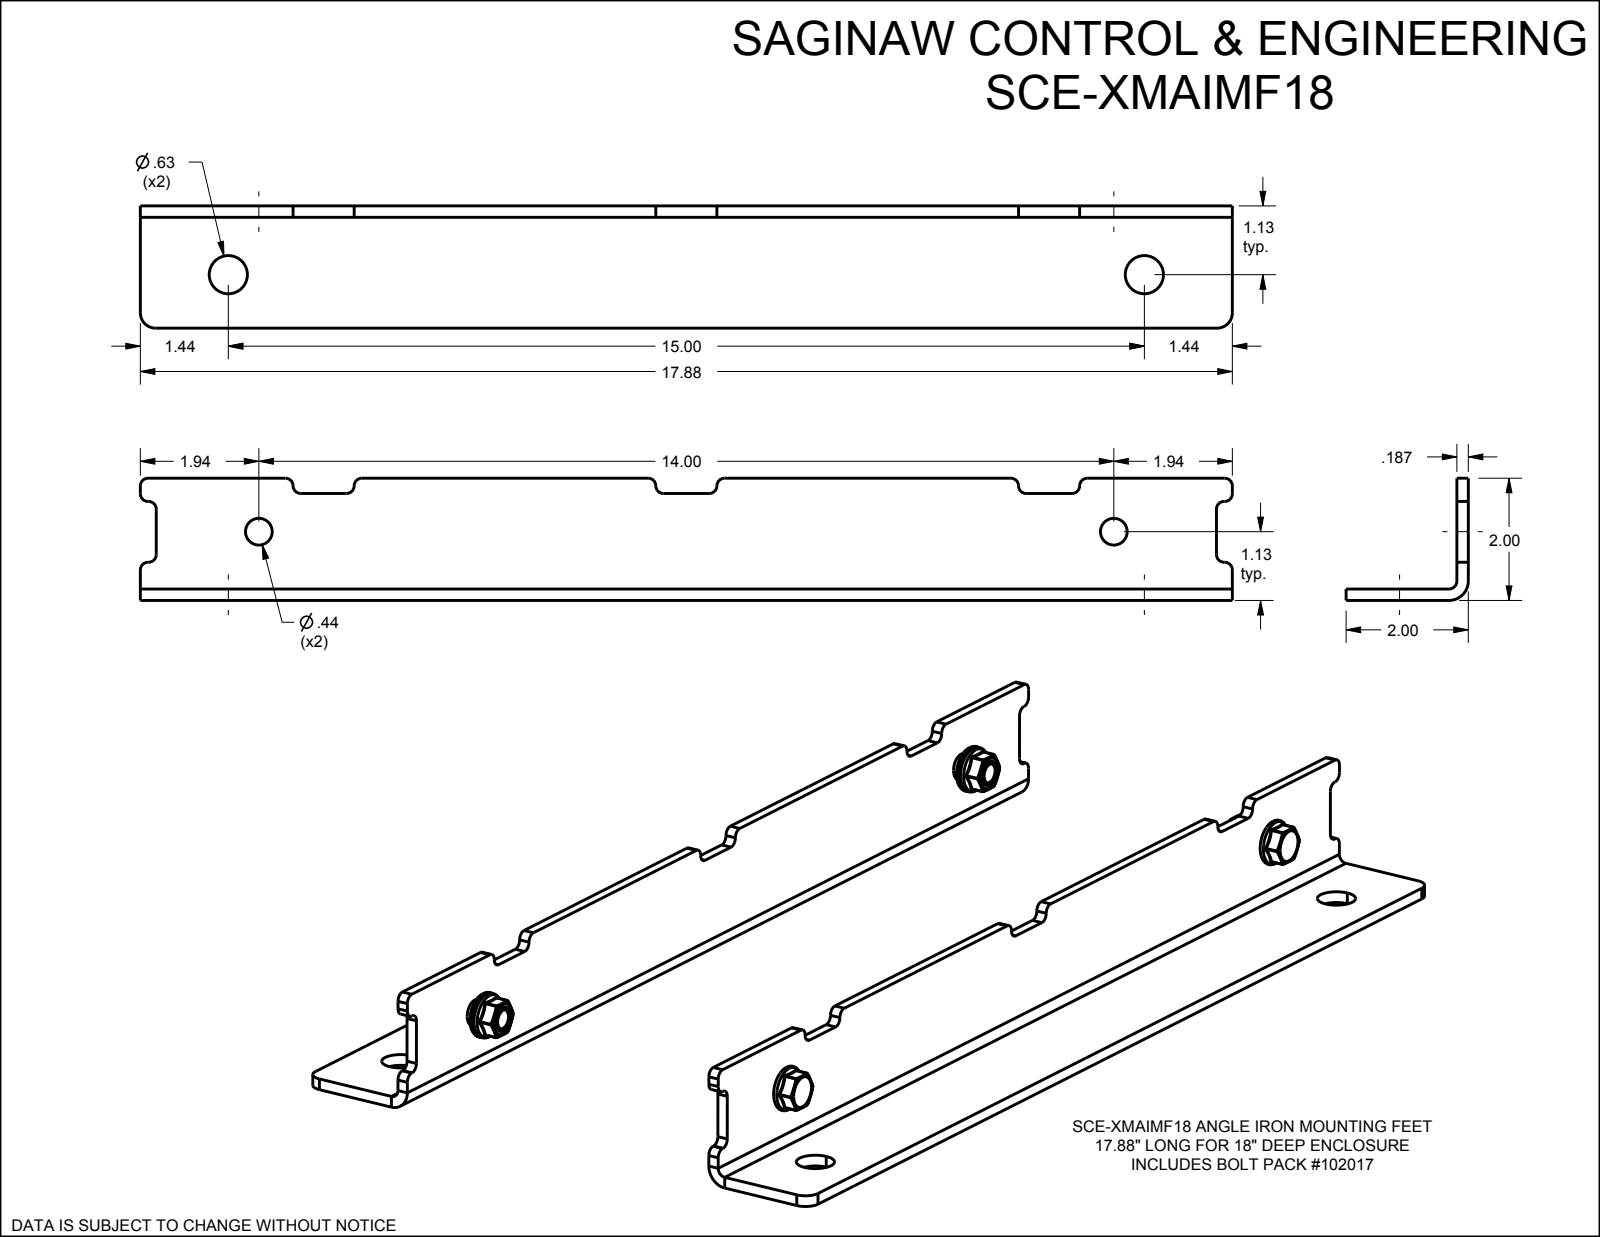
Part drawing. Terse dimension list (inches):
name: SCE-XMAIMF18
written by: SolidWorks 2019 (CONFIG_CONTROL_DESIGN)
unit: in
bodies: 14 solids, 488 faces (128 planar, 132 cylindrical, 228 other)
size: 17.875 × 10 × 2
volume: 25.11 in³; area: 295 in²
holes: 2× ⌀0.367, 2× ⌀0.4, 2× ⌀0.43, 2× ⌀0.437, 2× ⌀0.625, 2× ⌀0.625
bosses: 2× ⌀0.75, 2× ⌀0.7, 2× ⌀0.373
rounds: 22× R0.125, 18× R0.01, 4× R0.25, 2× R0.13, 2× R0.317
face distances: 0.187, 6.187, 6.374, 6, 1.813, 2, 8, 8.187, 10.001, 2.223
hole spacings: 8.25, 14.995, 17.115, 13.995, 14
